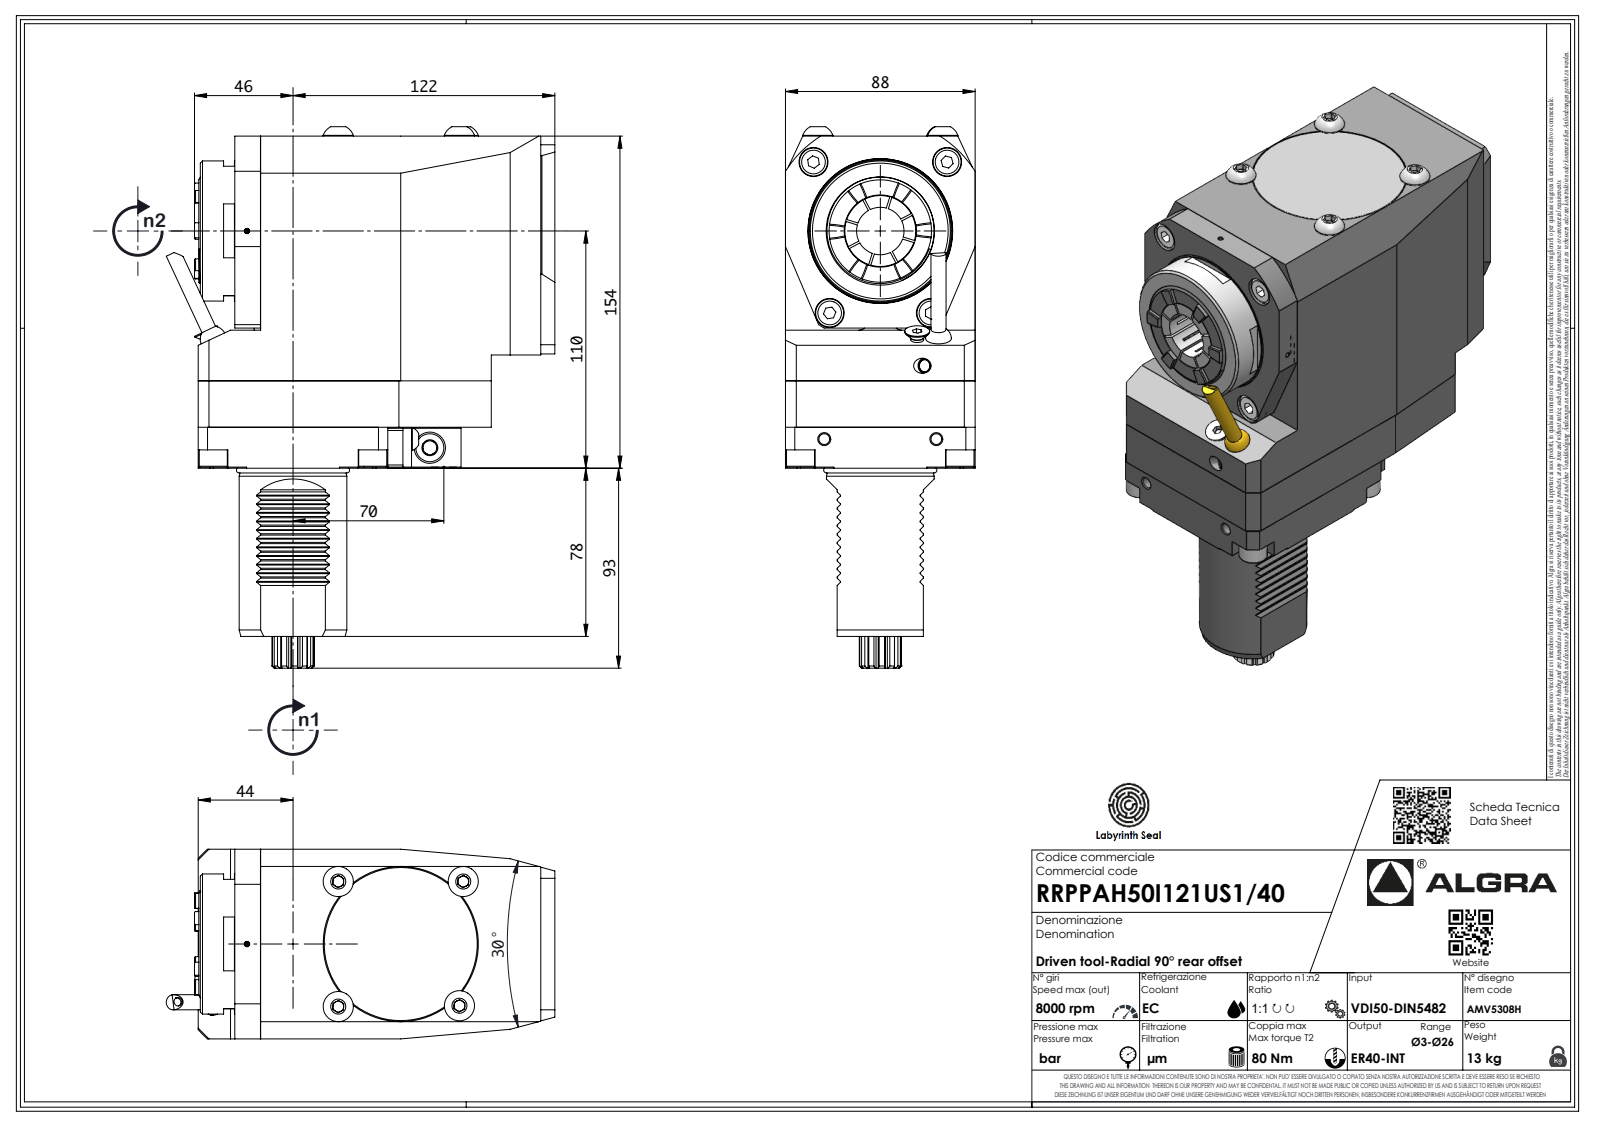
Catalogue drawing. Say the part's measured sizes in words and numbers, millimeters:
The part is named "RRPPAH50I121US140". Its 3-D file was written by "SolidWorks 2023 (AUTOMOTIVE_DESIGN)". It is 1 solid with 675 faces: 432 planar, 135 cylindrical and 108 other. Overall it measures 251.15 by 165.5 by 88 millimeters. Its volume is 2 018 000 cubic millimeters and its surface area 118 519 square millimeters. Round holes: 1 of diameter 2.1, 1 of diameter 10. Round bosses or shafts: 4 of diameter 14, 4 of diameter 13, 1 of diameter 65, 1 of diameter 50, 1 of diameter 48.7, 1 of diameter 6.37, 1 of diameter 1.7. Partial cylindrical surfaces (rounded edges, fillets, slot ends): 24 of radius 9.38, 22 of radius 0.3, 7 of radius 0.33, 7 of radius 0.52, 7 of radius 3.7, 4 of radius 1, 4 of radius 6.75, 2 of radius 4. The main face-to-face distances are 88, 135, 154, 165.5, 19, 1, 0.5, 17, 148.5, 18.5.
